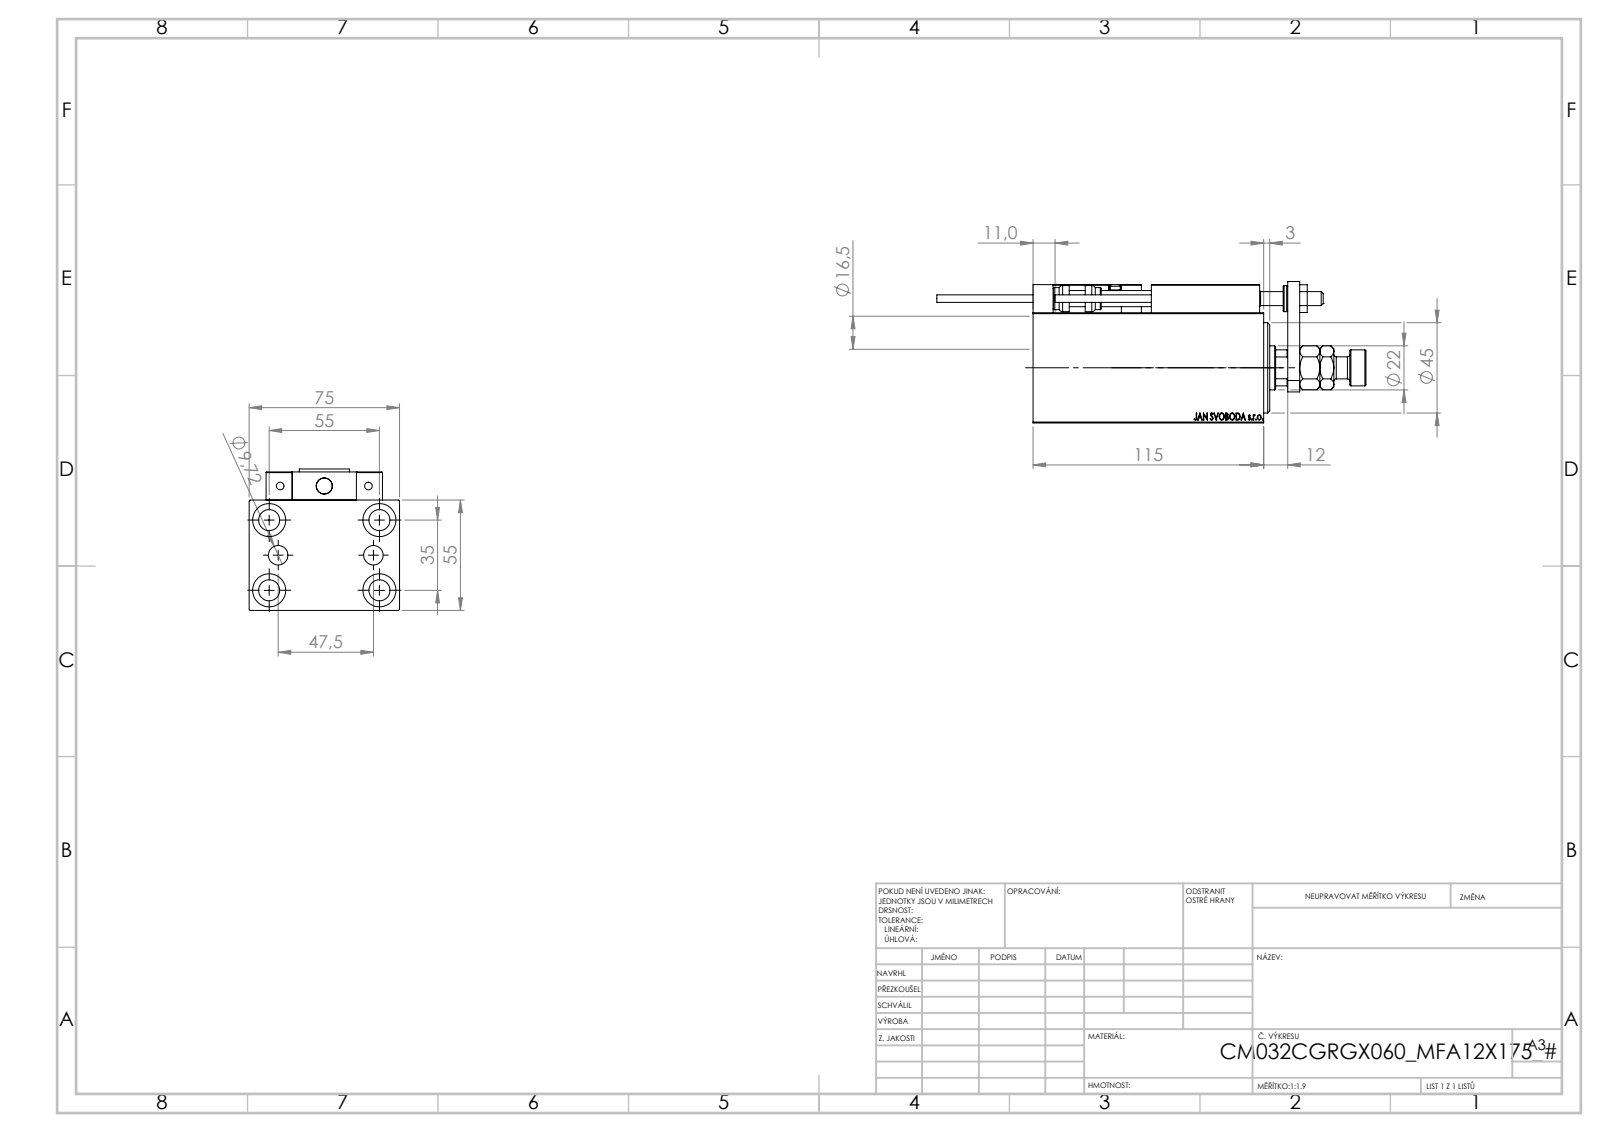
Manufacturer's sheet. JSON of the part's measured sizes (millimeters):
{"part_name": "ALLEN BOLT D8; SWITCH DIM B,W; SWITCH_X_FRONT_BACK; X_Y_MFA (+7 more)", "step_written_by": "SolidWorks 2019 (CONFIG_CONTROL_DESIGN)", "units": "millimeters", "bodies": {"solids": 24, "faces": 1330, "planar": 576, "cylindrical": 188, "other": 566}, "overall_size": [214, 75, 70.5], "volume_mm3": 457237, "surface_area_mm2": 108420, "round_holes": [[4, 6], [8, 5], [10.5, 5], [16.5, 5], [3.2, 4], [5, 2], [9.72, 2], [7, 1], [22, 1], [25.5, 1], [32, 1], [34, 1]], "round_bosses_or_shafts": [[11, 2], [5, 2], [3.8, 2], [18, 1], [13, 1]], "partial_cylinders_radius": [[0.3, 30], [3, 2], [10.5, 1]], "face_to_face_distances": [55, 75, 14, 5, 3, 69, 23, 18, 10, 12], "hole_center_spacings": [17.9, 32.6, 54.16, 11.37, 20, 23.75, 29.59, 29.69]}
